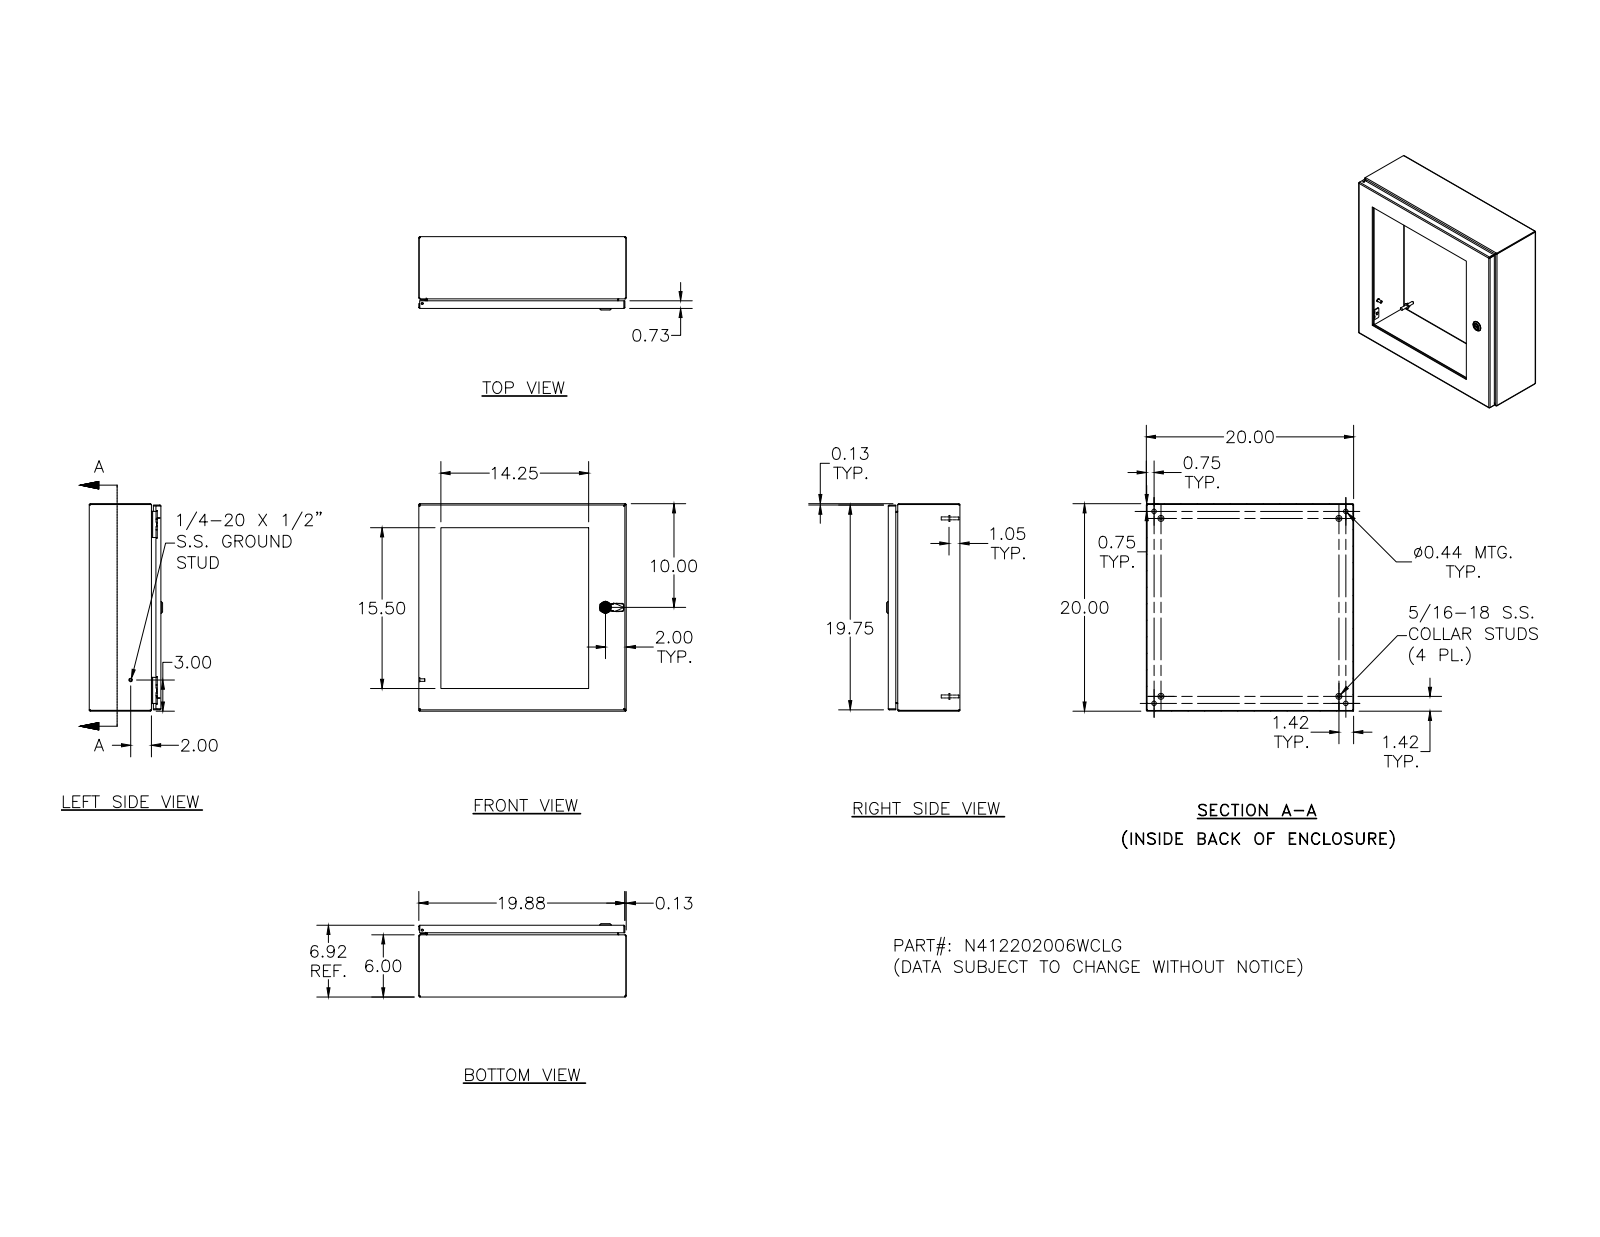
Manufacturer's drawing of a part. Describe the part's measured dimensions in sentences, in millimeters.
The part is named "N412202006WCLG". Its 3-D file was written by "SolidWorks 2018 (AUTOMOTIVE_DESIGN)". It is 69 solids with 2019 faces: 753 planar, 617 cylindrical and 649 other. Overall it measures 508 by 508 by 179.7 millimeters. Its volume is 2 602 000 cubic millimeters and its surface area 2 030 000 square millimeters. Round holes: 18 of diameter 4, 16 of diameter 7.1, 5 of diameter 4.8, 4 of diameter 2.4, 4 of diameter 3.9, 4 of diameter 4.2, 4 of diameter 4.4, 4 of diameter 11.1, 1 of diameter 4.7, 1 of diameter 5, 1 of diameter 8, 1 of diameter 10. Round bosses or shafts: 16 of diameter 8.6, 16 of diameter 4.8, 10 of diameter 6.4, 4 of diameter 14.3, 4 of diameter 9.1, 4 of diameter 8.1, 4 of diameter 7.6, 4 of diameter 7. Partial cylindrical surfaces (rounded edges, fillets, slot ends): 34 of radius 0.8, 30 of radius 0.3, 26 of radius 1.3, 24 of radius 2.7, 18 of radius 0.4, 16 of radius 3.2, 13 of radius 0.5, 8 of radius 0.8. The main face-to-face distances are 1.9, 173.8, 506.1, 171.9, 6.4, 167.5, 165.6, 508, 504.2, 175.7. The hole center spacings are 101.6, 203.2, 406.6, 406.4, 437.4, 158, 218.1, 254.9.
